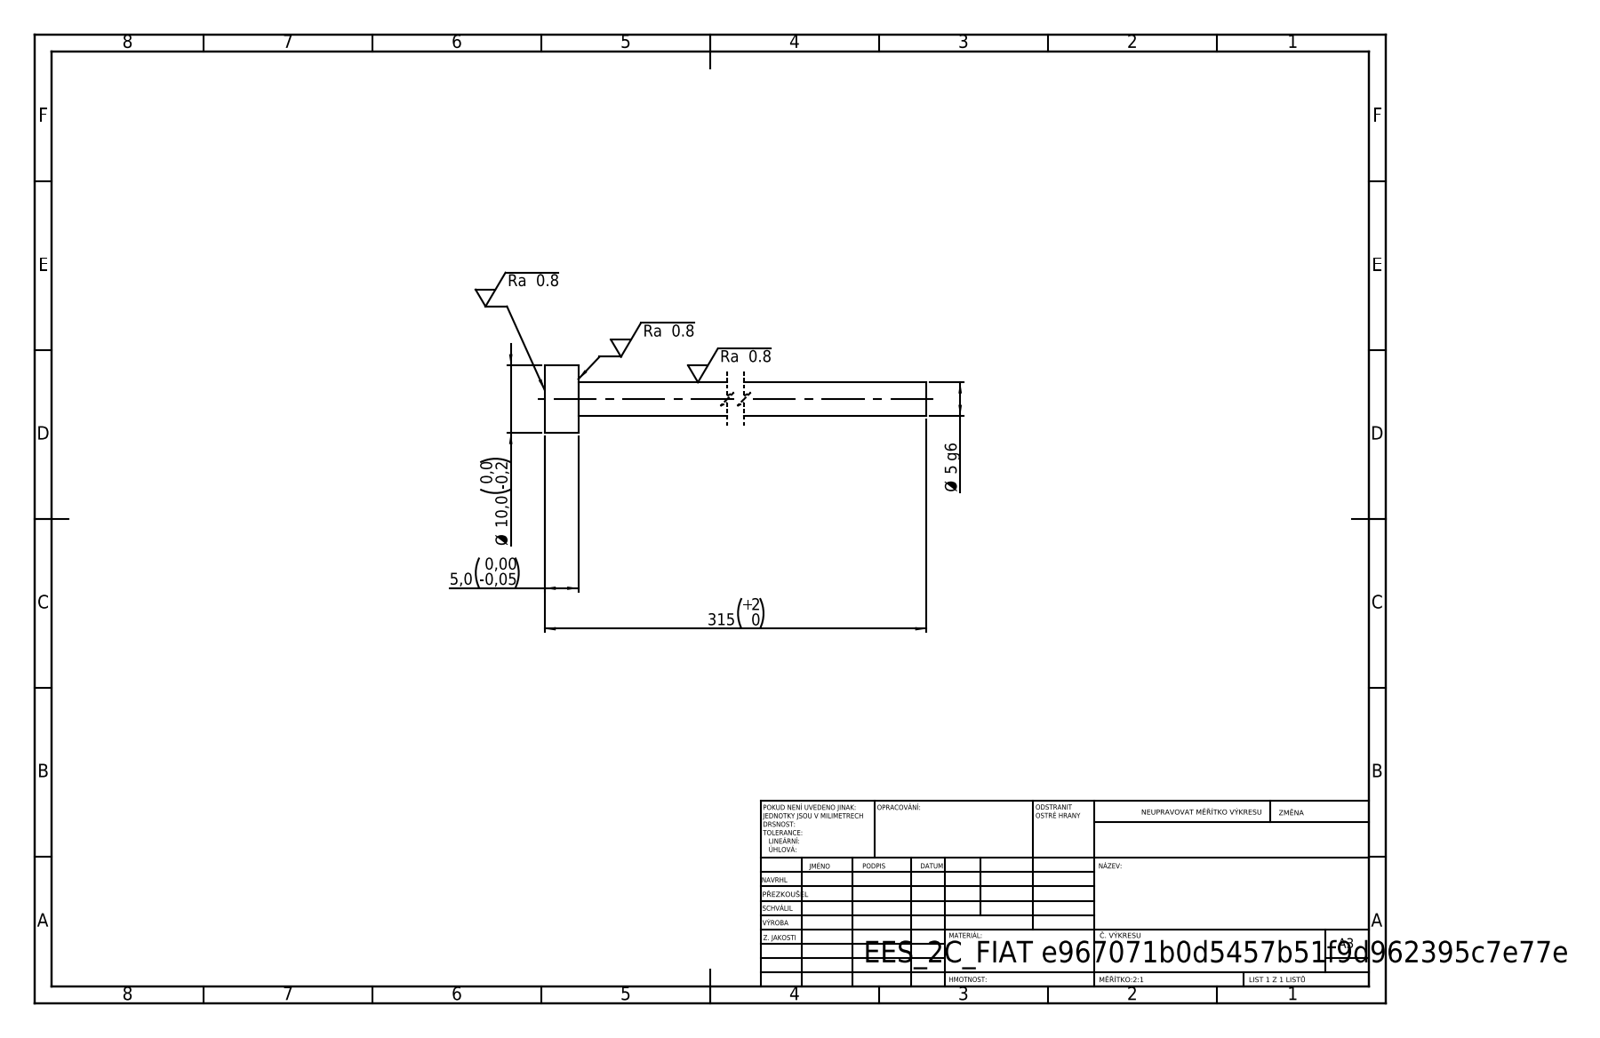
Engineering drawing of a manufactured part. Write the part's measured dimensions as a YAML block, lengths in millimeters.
step_written_by: "SolidWorks 2019 (CONFIG_CONTROL_DESIGN)"
units: millimeters
bodies: {solids: 1, faces: 7, planar: 3, cylindrical: 4, other: 0}
overall_size: [315, 10, 10]
volume: 6480
surface_area: 5184
round_bosses_or_shafts:
  - {diameter: 10, count: 1}
  - {diameter: 5, count: 1}
face_to_face_distances: [5, 315, 310]
